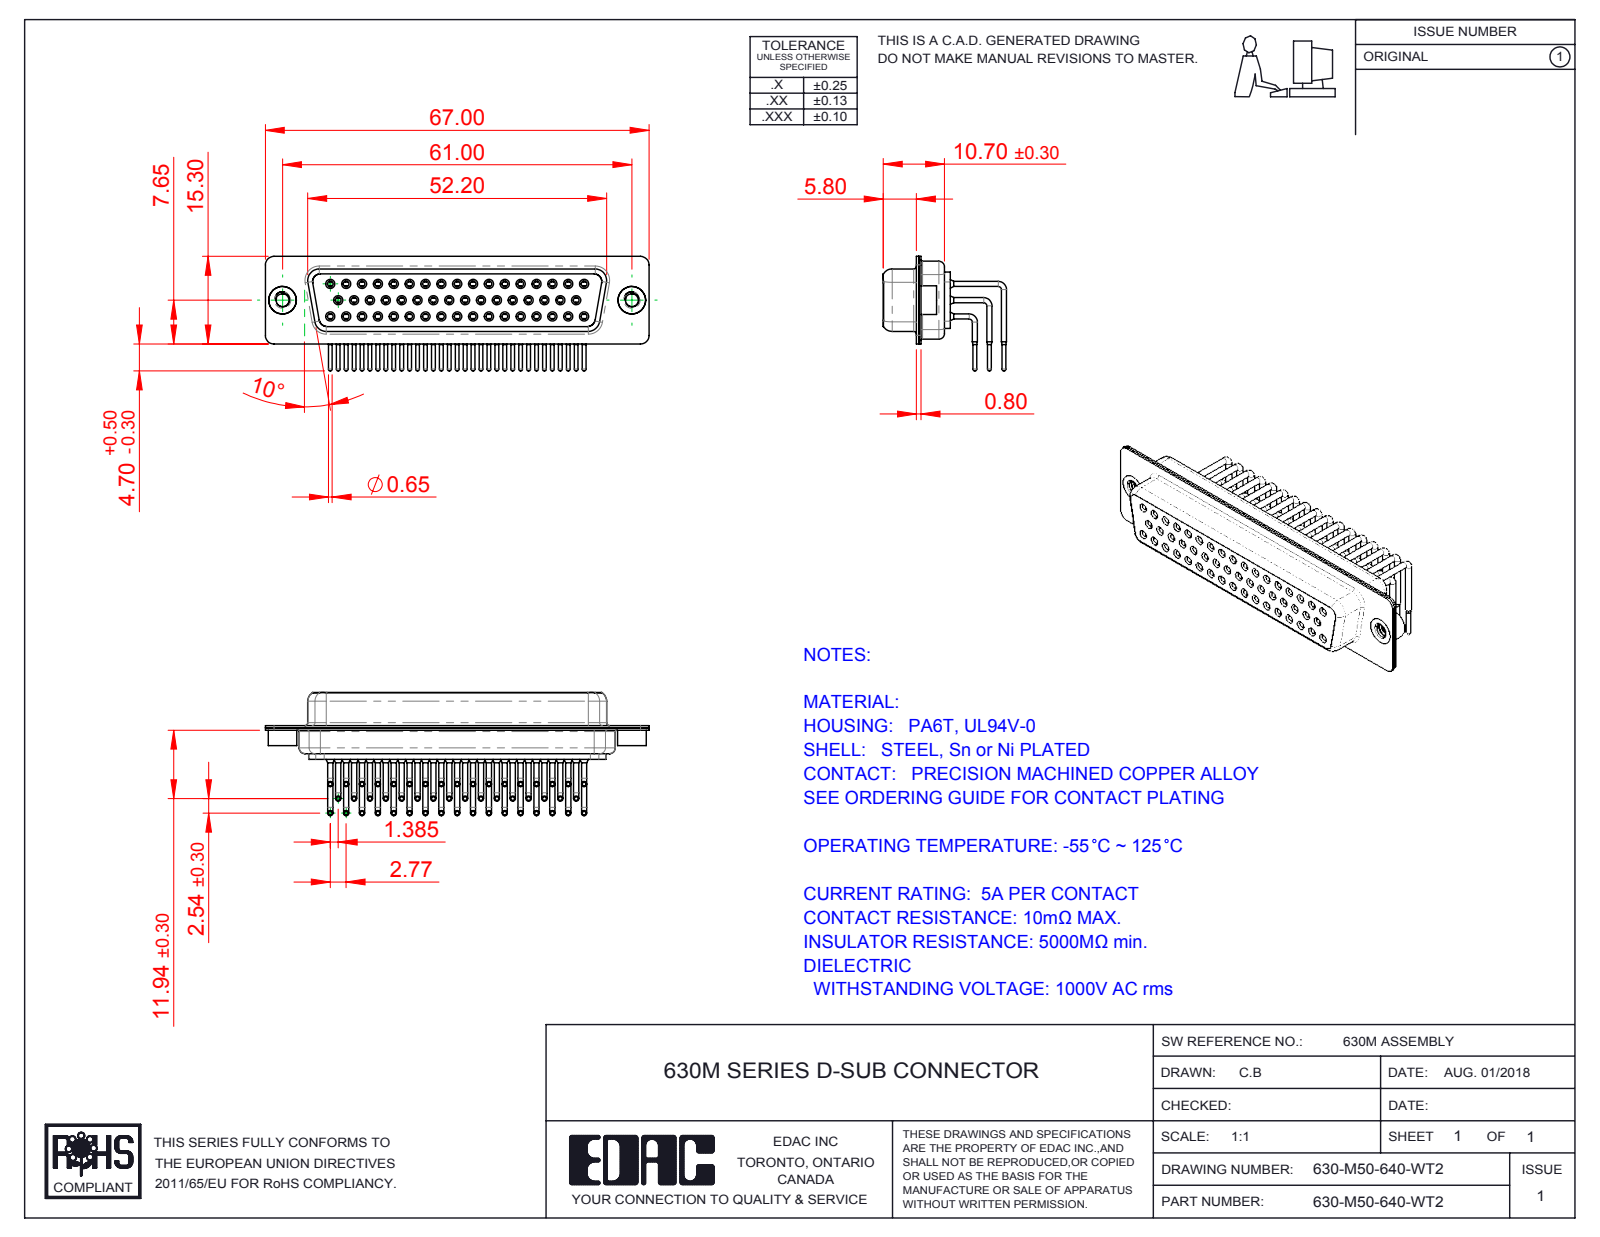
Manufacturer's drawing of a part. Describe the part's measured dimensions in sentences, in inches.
The part is named "630-M50-640-WT2; 630M Contact Row 1_50 Contacts; 630M Shell Rear_50 Contacts; 630M Shell Front_50 Contacts (+4 more)". Its 3-D file was written by "SolidWorks 2016 (CONFIG_CONTROL_DESIGN)". It is 55 solids with 2929 faces: 817 planar, 1287 cylindrical and 825 other. Overall it measures 2.638 by 0.848 by 0.787 inches. Its volume is 0.428 cubic inches and its surface area 25.67 square inches. Round holes: 50 of diameter 0.039, 50 of diameter 0.043, 50 of diameter 0.067, 50 of diameter 0.071, 50 of diameter 0.079, 2 of diameter 0.089, 2 of diameter 0.157, 2 of diameter 0.189. Round bosses or shafts: 100 of diameter 0.035, 50 of diameter 0.063, 50 of diameter 0.059, 50 of diameter 0.026, 2 of diameter 0.197, 2 of diameter 0.193. Partial cylindrical surfaces (rounded edges, fillets, slot ends): 16 of radius 0.059, 12 of radius 0.079, 8 of radius 0.053, 8 of radius 0.063, 4 of radius 0.01, 4 of radius 0.02, 4 of radius 0.024, 4 of radius 0.026. The main face-to-face distances are 0.016, 0.053, 0.467, 0.033, 0.087, 0.217, 0.482, 0.232, 0.413, 0.031. The hole center spacings are 0.109, 0.124, 0.218, 0.327, 0.436, 0.545, 0.654, 0.763.
